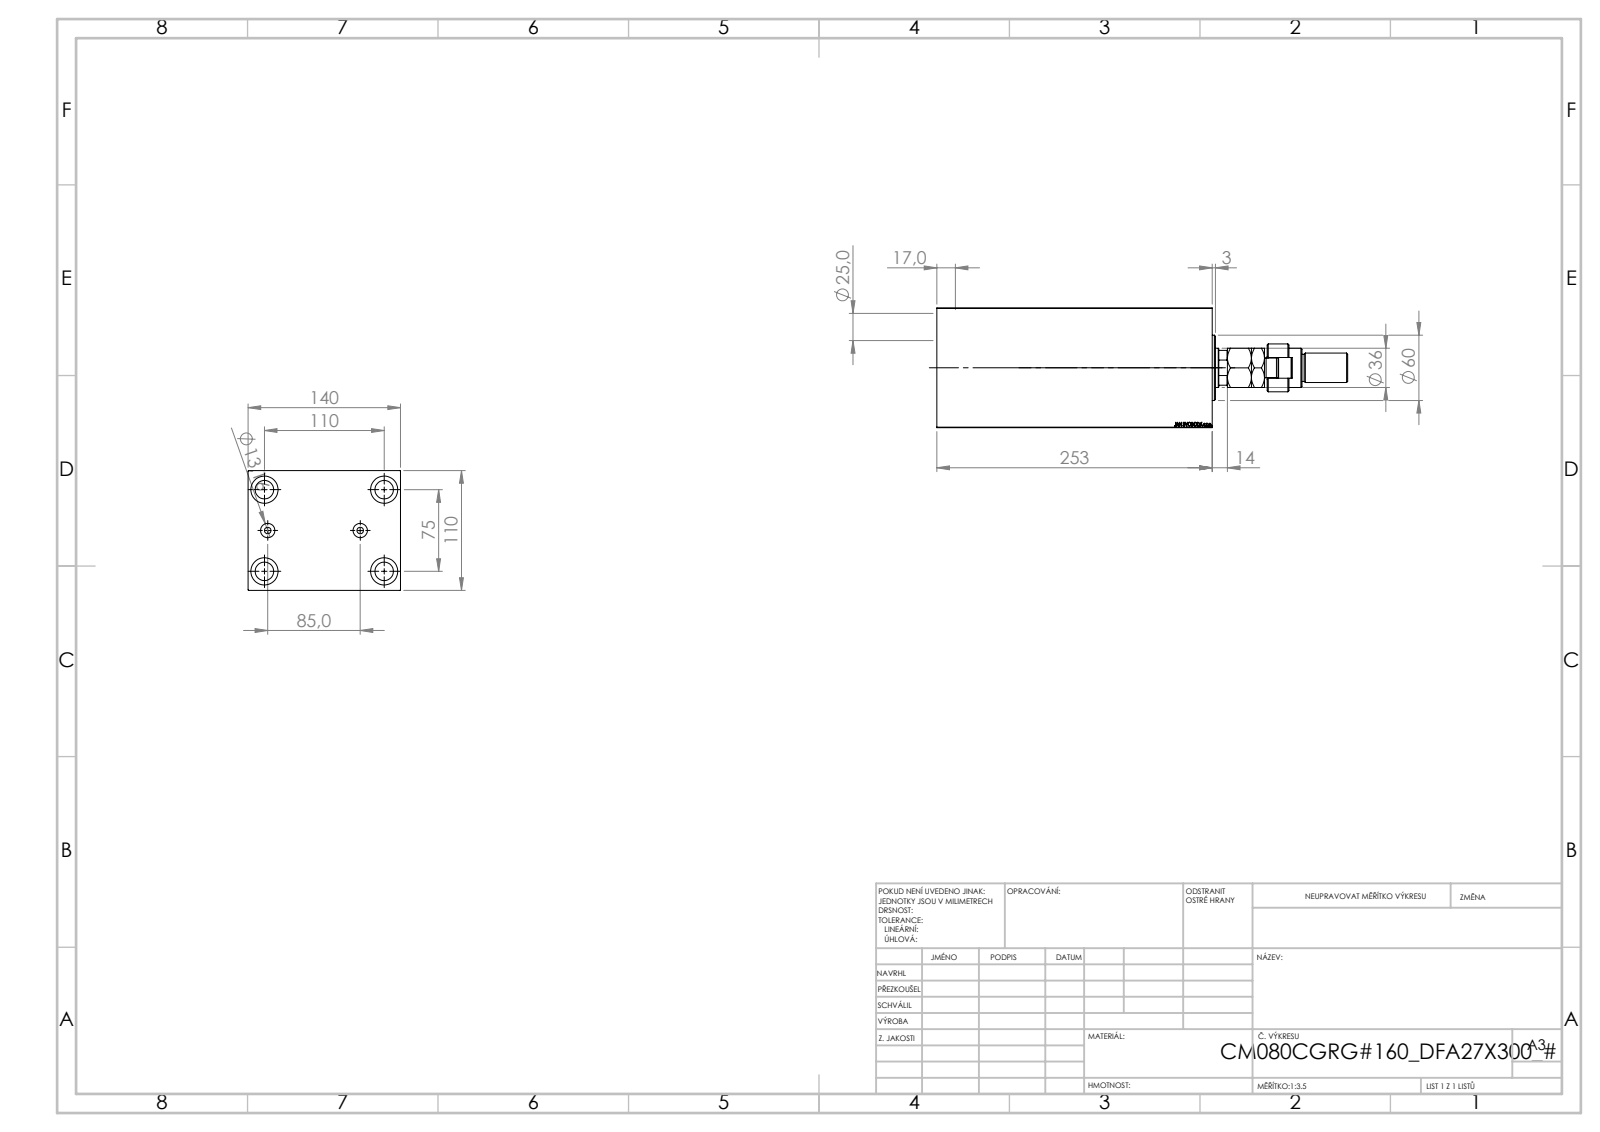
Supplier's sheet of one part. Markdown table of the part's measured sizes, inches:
| quantity | value |
| --- | --- |
| part name | V450CM_C_Body; V450CM_VC_B; V450CM_C_VCP; MFA (+1 more) |
| STEP written by | SolidWorks 2019 (CONFIG_CONTROL_DESIGN) |
| units | inches |
| bodies | 5 solids, 948 faces (439 planar, 71 cylindrical, 438 other) |
| overall size | 14.862 × 5.512 × 4.331 |
| volume | 187.5 in³ |
| surface area | 571.3 in² |
| round holes (diameter × count) | 0.669 × 4, 0.984 × 4, 0.236 × 2, 0.518 × 2, 1.004 × 1, 1.555 × 1, 3.15 × 1, 3.228 × 1, 3.425 × 1 |
| round bosses / shafts (diameter × count) | 2.362 × 1, 1.732 × 1, 1.417 × 1, 1.102 × 1, 1.063 × 1, 0.984 × 1, 0.709 × 1 |
| partial cylindrical surfaces (radius × count) | 0.374 × 1, 0.591 × 1, 0.689 × 1 |
| main face-to-face distances | 4.331, 5.512, 9.961, 9.134, 0.827, 1.469, 7.665, 8.492, 7.768, 6.299 |
| hole center spacings | 1.556, 2.621, 4.113, 1.673, 2.953, 4.331, 5.242, 3.346 |
